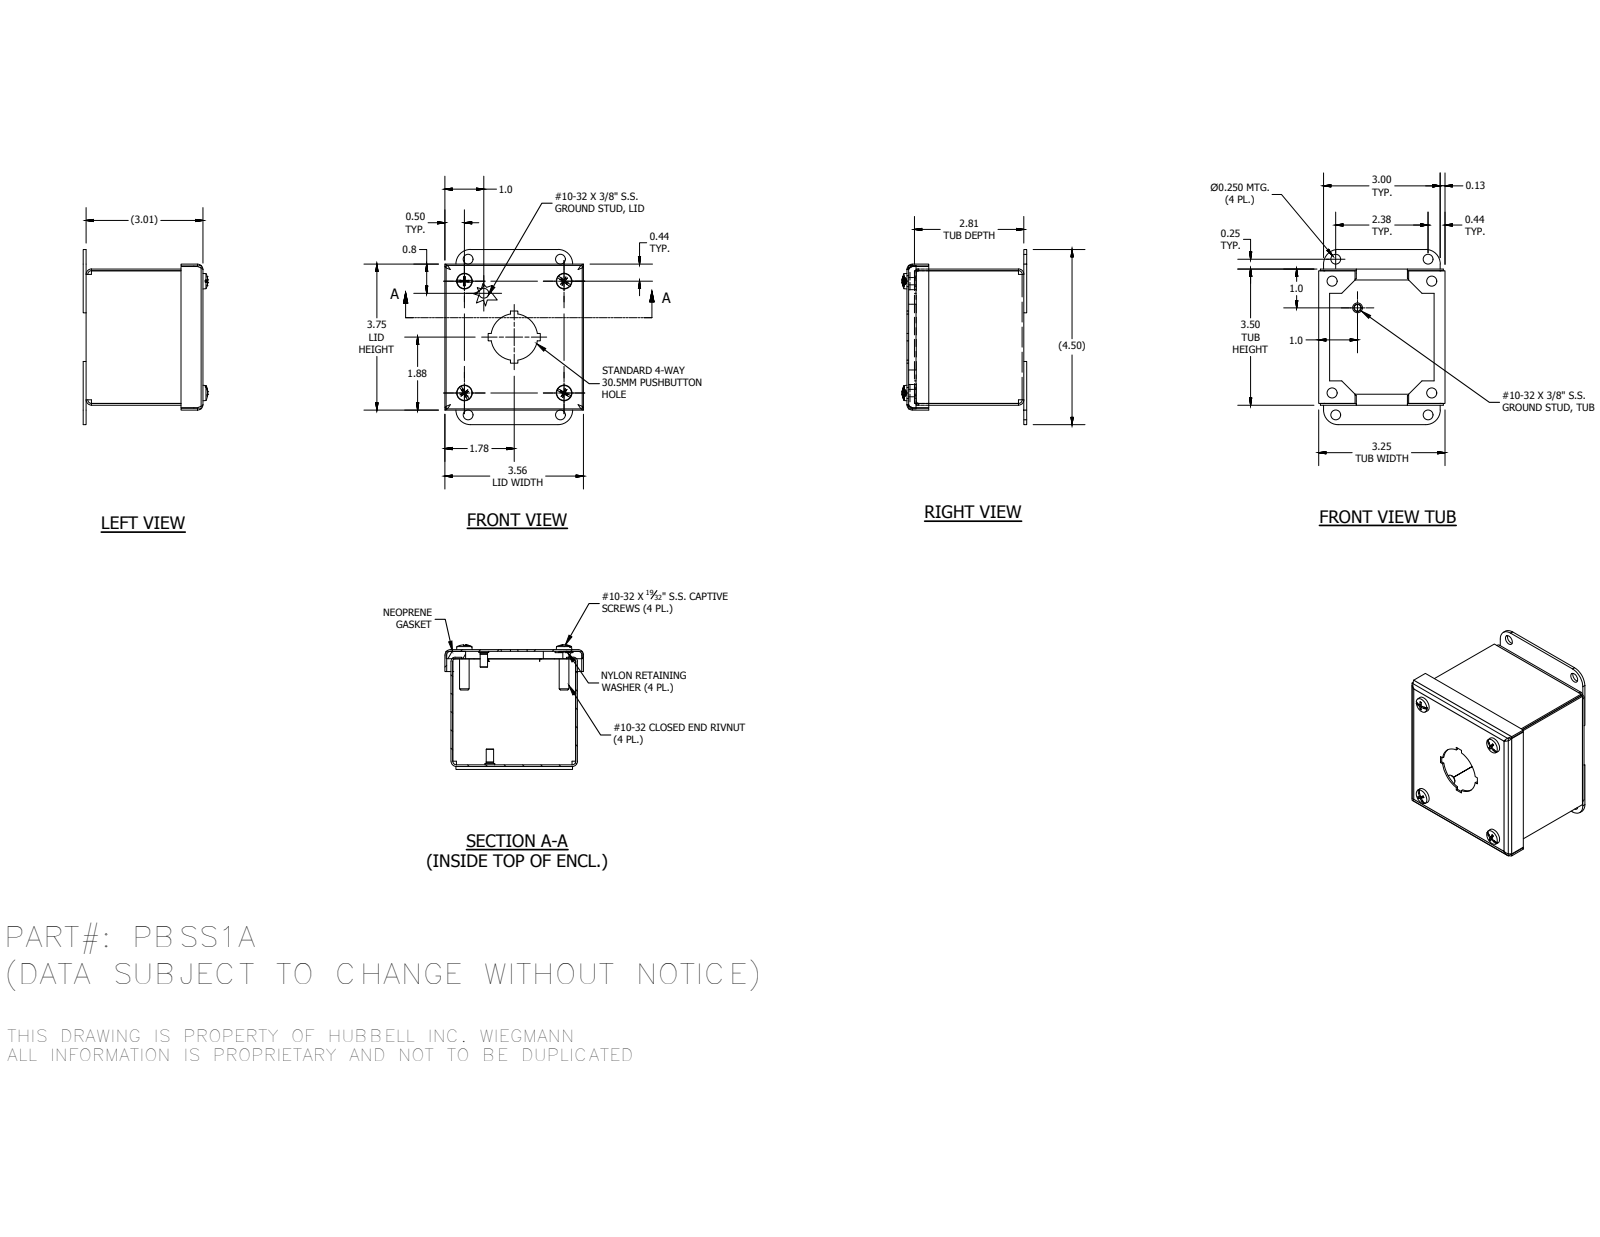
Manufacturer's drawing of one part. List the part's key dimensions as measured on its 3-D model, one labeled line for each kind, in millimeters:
Part name (STEP PRODUCT): PBSS1ALID; 37210; 39077; PBSS1ABKP (+5 more)
STEP written by: Autodesk Inventor 2016 (CONFIG_CONTROL_DESIGN)
Units: millimetres
Bodies: 19 solids, 542 faces (334 planar, 100 cylindrical, 108 other)
Overall size (bounding box): 114.3 × 90.49 × 81.29
Volume: 85 700 mm³ · Surface area: 121 552 mm²
Round holes (diameter × count): ⌀3.96 ×4, ⌀4.98 ×4, ⌀6.35 ×4, ⌀6.53 ×4, ⌀7.06 ×4, ⌀7.14 ×4, ⌀7.95 ×4, ⌀3.38 ×2, ⌀30.48 ×1
Round bosses / shafts (diameter × count): ⌀11.51 ×4, ⌀10.31 ×4, ⌀6.3 ×4, ⌀4.25 ×4, ⌀6.35 ×2, ⌀4.83 ×2
Partial cylindrical surfaces — rounded edges, fillets, slot ends (radius × count): R2.38 ×8, R3.52 ×8, R2.27 ×4, R9.53 ×4, R1.59 ×2, R1.59 ×2, R2.73 ×2, R2.73 ×2
Main face-to-face distances: 1.14, 1.15, 75.19, 87.76, 76.33, 75.18, 74.04, 78.21, 77.07, 3.03
Hole centre spacings: 48.91, 87.34, 1.58, 1.59, 14.48, 14.49, 16.05, 16.06
